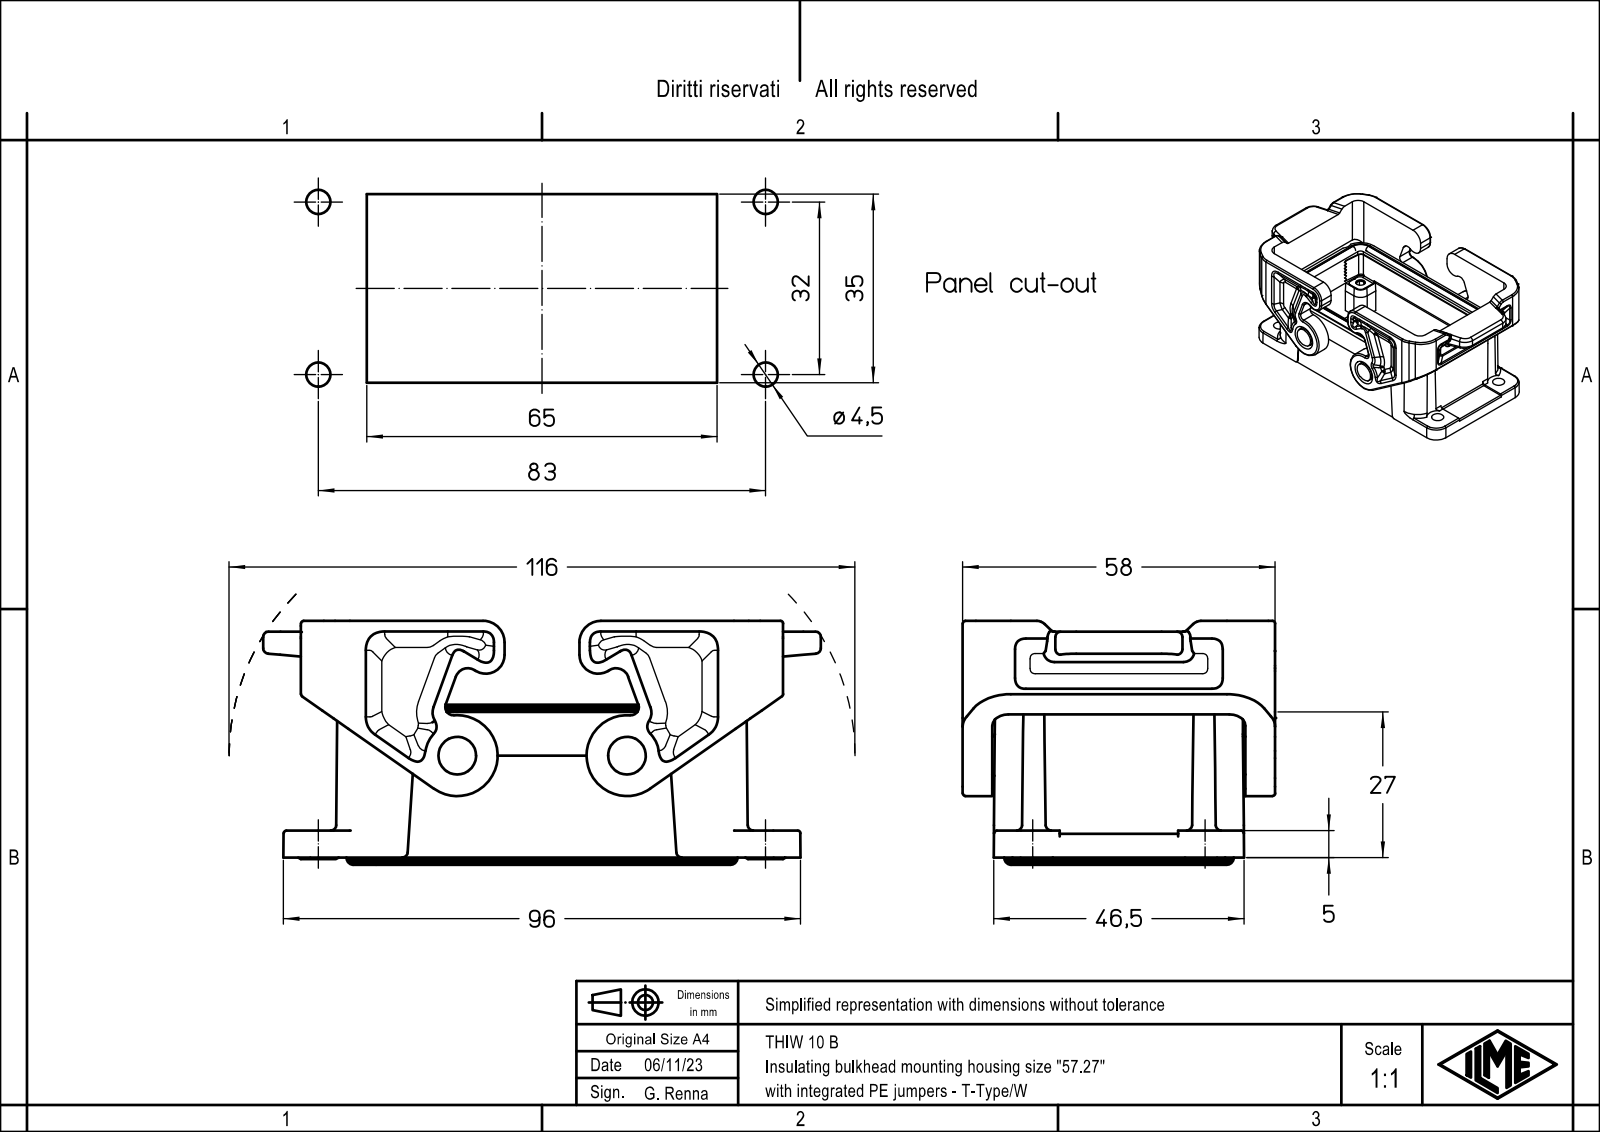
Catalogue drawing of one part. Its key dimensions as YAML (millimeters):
part_name: "THIW 10 B"
step_written_by: "Creo Elements/Direct Modeling 20.1B 02-Apr-2019 (C) Parametric Technology GmbH (AUTOMOTIVE_DESIGN)"
units: millimeters
bodies: {solids: 1, faces: 821, planar: 404, cylindrical: 249, other: 168}
overall_size: [103.5, 58, 45.25]
volume: 64813
surface_area: 37556
round_holes:
  - {diameter: 2.5, count: 4}
  - {diameter: 3.5, count: 4}
  - {diameter: 4.5, count: 4}
  - {diameter: 7.2, count: 2}
round_bosses_or_shafts:
  - {diameter: 4.8, count: 4}
  - {diameter: 7, count: 2}
partial_cylinders:
  - {radius: 1, count: 25}
  - {radius: 1.3, count: 20}
  - {radius: 1.5, count: 18}
  - {radius: 2, count: 16}
  - {radius: 3, count: 12}
  - {radius: 5.5, count: 12}
  - {radius: 5, count: 8}
  - {radius: 6, count: 8}
face_to_face_distances: [40.6, 5.5, 52.5, 47, 40.4, 70.61, 45.9, 6.3, 46.2, 11.8]
hole_center_spacings: [13.24, 32.24, 70.04, 75.96, 27, 32, 57, 63.07]
